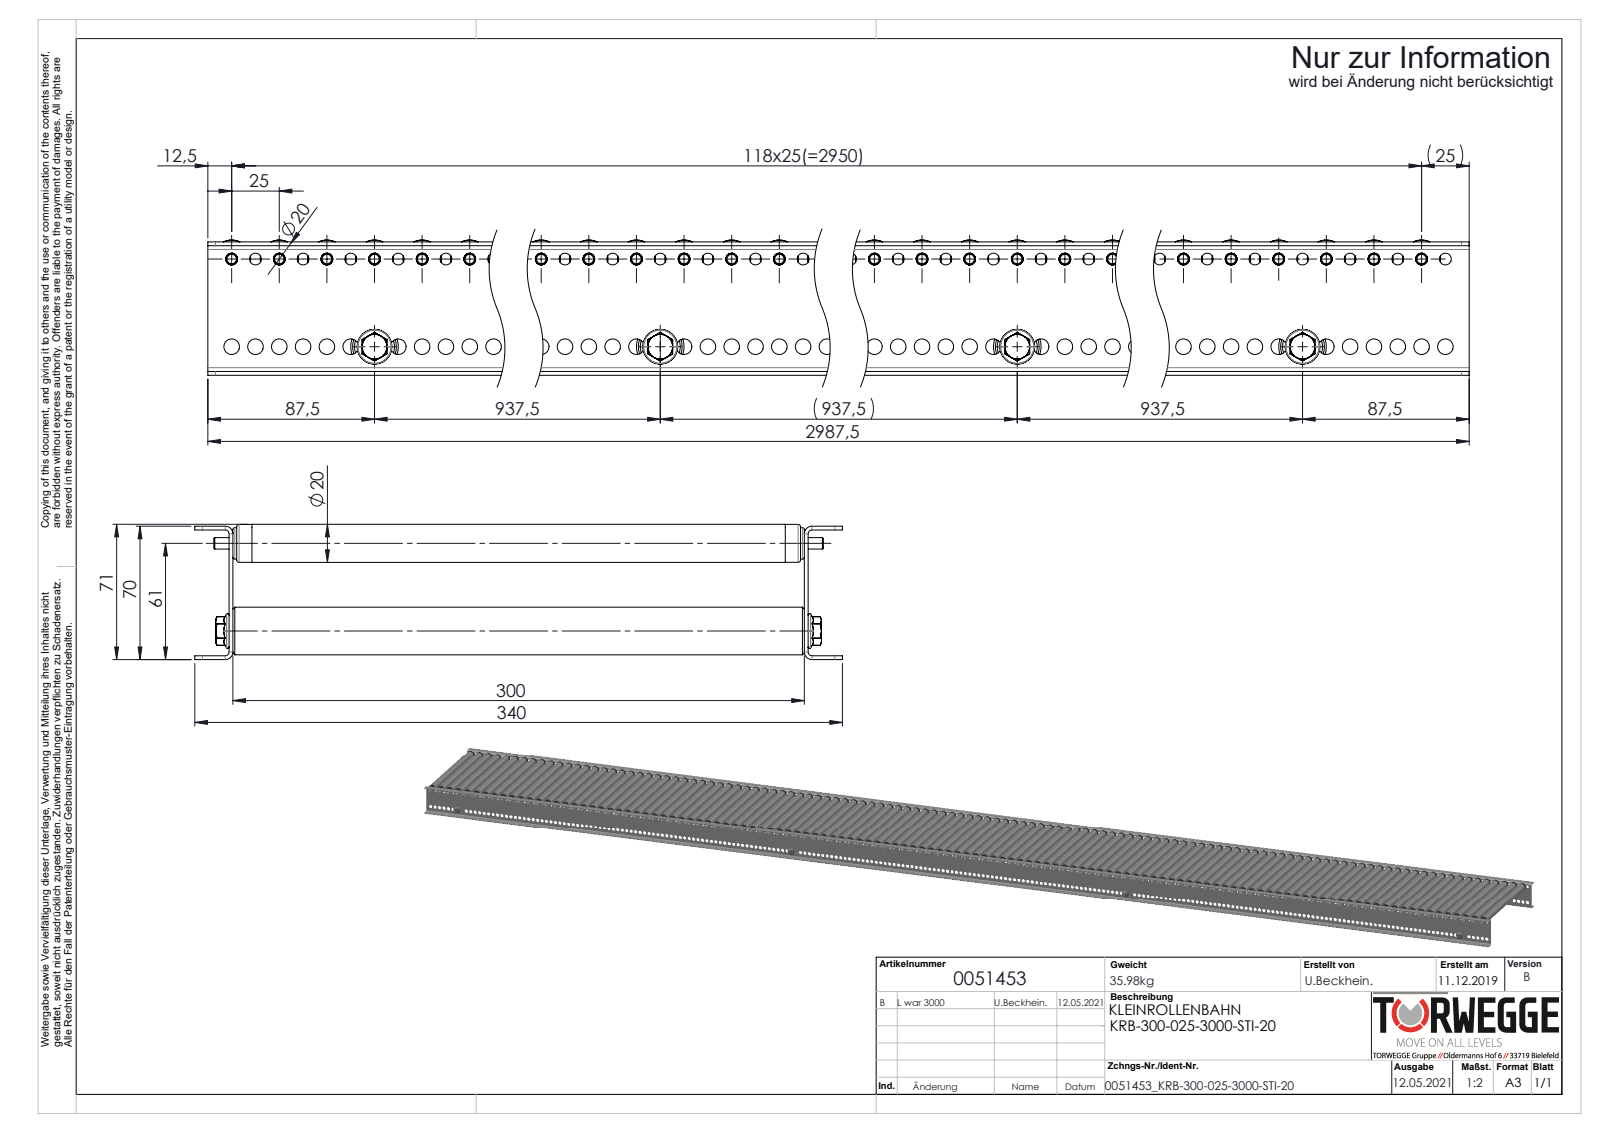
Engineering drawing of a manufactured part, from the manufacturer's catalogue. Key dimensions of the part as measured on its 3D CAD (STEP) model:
Part name (STEP PRODUCT): S100992_Typ-KUT50-20x1-6; KUT50-20x1,5-STI-A6_FA-EL=KFG_S100909_KUT50-20x1-STI-A6-FA-EL=300; 0039777_Achse-Ø06-FA-KFG_L=320 fr D20; Profil_KRB-20x70x20x2_KFG_S109089_U-PROFIL-20-70-20-2-KRB-20-L=2987,5 (+4 more)
STEP written by: SolidWorks 2020 (AUTOMOTIVE_DESIGN)
Units: millimetres
Bodies: 260 solids, 23356 faces (7582 planar, 8902 cylindrical, 6872 other)
Overall size (bounding box): 2987.5 × 340 × 71
Volume: 4 452 000 mm³ · Surface area: 6 899 000 mm²
Round holes (diameter × count): ⌀6.2 ×238, ⌀8.2 ×238, ⌀6.1 ×119, ⌀14.2 ×119, ⌀17.2 ×119, ⌀18 ×119, ⌀6.8 ×4, ⌀21 ×4
Round bosses / shafts (diameter × count): ⌀20 ×119, ⌀19.9 ×119, ⌀18.1 ×119, ⌀17.8 ×119, ⌀16.5 ×119, ⌀6 ×119, ⌀25 ×4, ⌀8 ×4
Partial cylindrical surfaces — rounded edges, fillets, slot ends (radius × count): R4.05 ×119, R4 ×8, R2 ×4
Main face-to-face distances: 2, 302, 68, 300, 304, 70, 66, 292, 18, 30
Hole centre spacings: 12.5, 25, 37.5, 50, 62.5, 75, 87.5, 100
